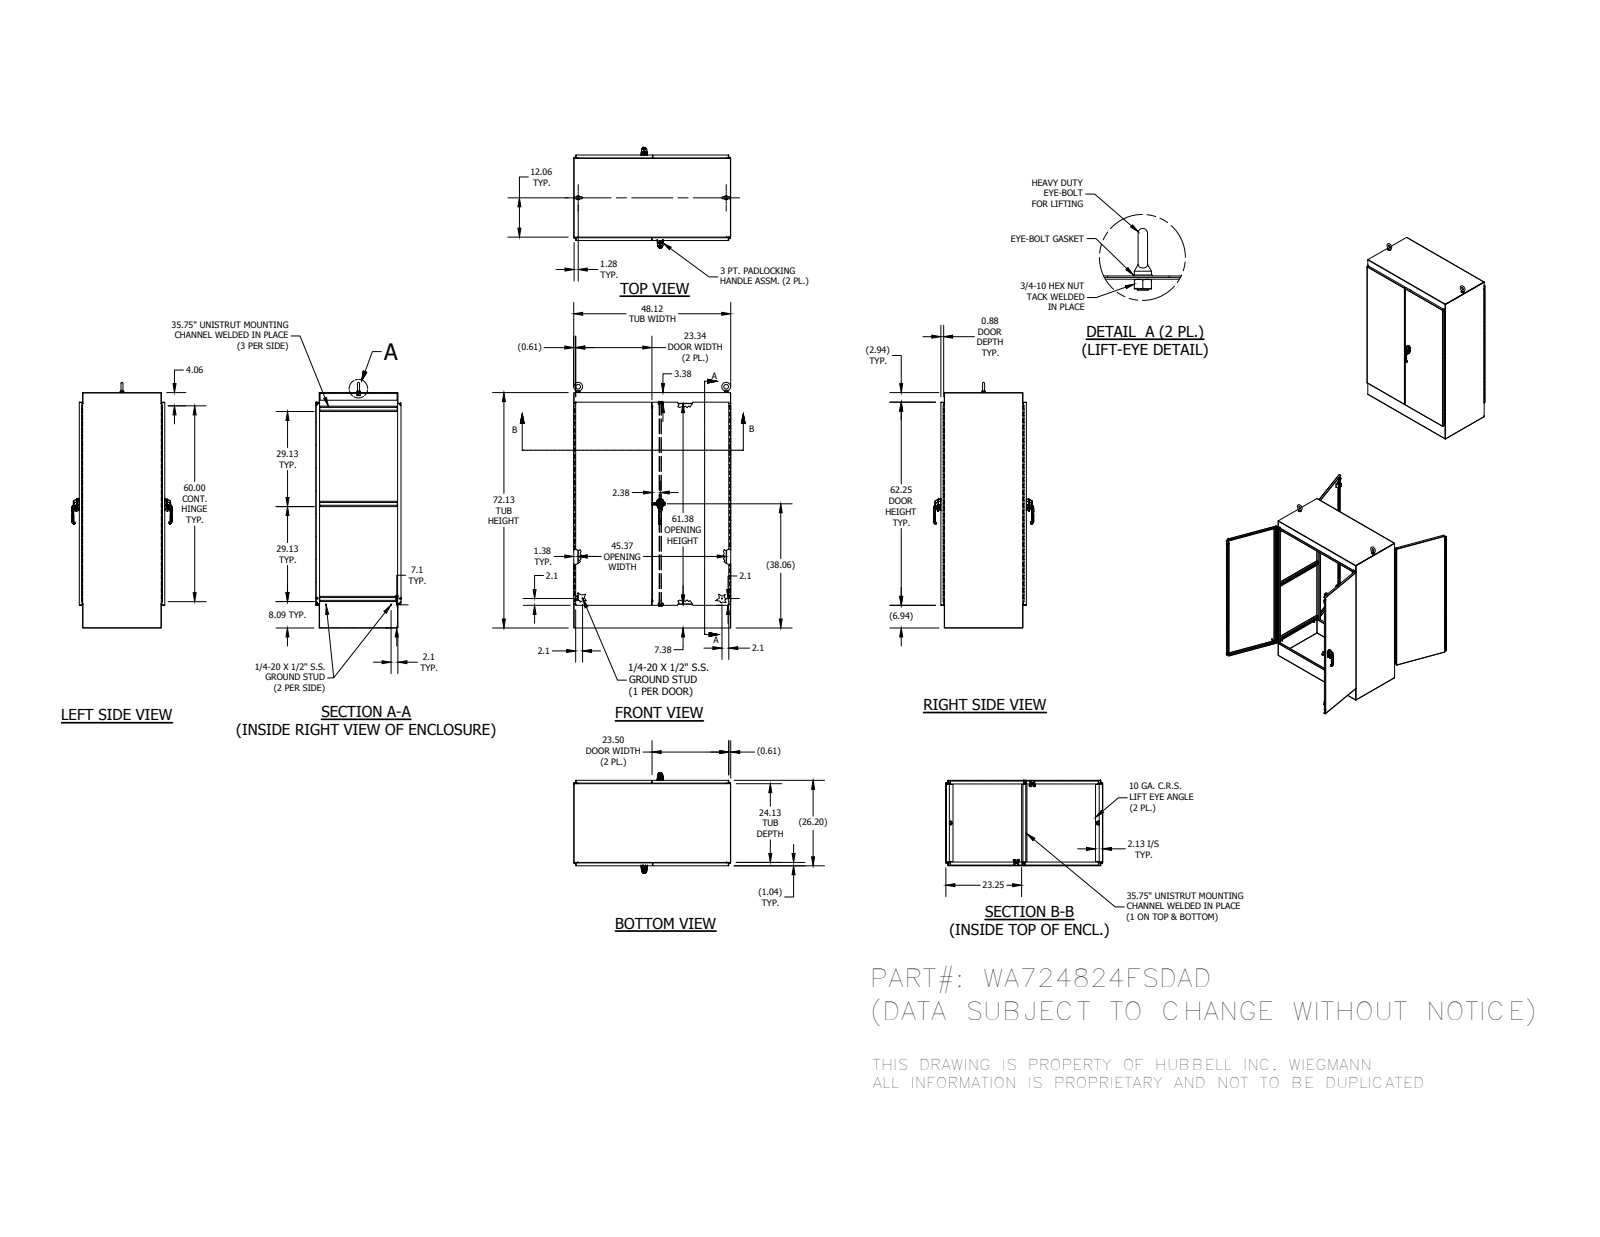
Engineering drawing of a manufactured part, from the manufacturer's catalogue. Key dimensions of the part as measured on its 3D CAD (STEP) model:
Part name (STEP PRODUCT): FUN00103; HFW3025; 316298; 349132 (+8 more)
STEP written by: Autodesk Inventor 2014 (AUTOMOTIVE_DESIGN)
Units: millimetres
Bodies: 110 solids, 7244 faces (3406 planar, 2450 cylindrical, 1388 other)
Overall size (bounding box): 1911.29 × 1222.38 × 780.62
Volume: 26 220 000 mm³ · Surface area: 21 460 000 mm²
Round holes (diameter × count): ⌀7.02 ×16, ⌀5.08 ×8, ⌀5.4 ×6, ⌀6 ×6, ⌀7.11 ×6, ⌀3.17 ×4, ⌀6.13 ×4, ⌀6.35 ×4, ⌀6.41 ×4, ⌀10.16 ×4, ⌀10.33 ×4, ⌀10.5 ×4
Round bosses / shafts (diameter × count): ⌀6.35 ×8, ⌀25.4 ×4, ⌀14.29 ×4, ⌀13.37 ×4, ⌀12.7 ×4, ⌀9.52 ×4, ⌀8.56 ×4, ⌀7.94 ×4
Partial cylindrical surfaces — rounded edges, fillets, slot ends (radius × count): R0.5 ×345, R0.3 ×167, R0.79 ×46, R0.47 ×38, R0.25 ×32, R2 ×30, R3.17 ×30, R1.27 ×28
Main face-to-face distances: 2.38, 662.99, 1220, 660.61, 665.37, 26.3, 636.69, 1829.6, 1217.62, 1222.38
Hole centre spacings: 6.5, 12.5, 22.5, 51.5, 124.7, 126.71, 981.95, 9.66
